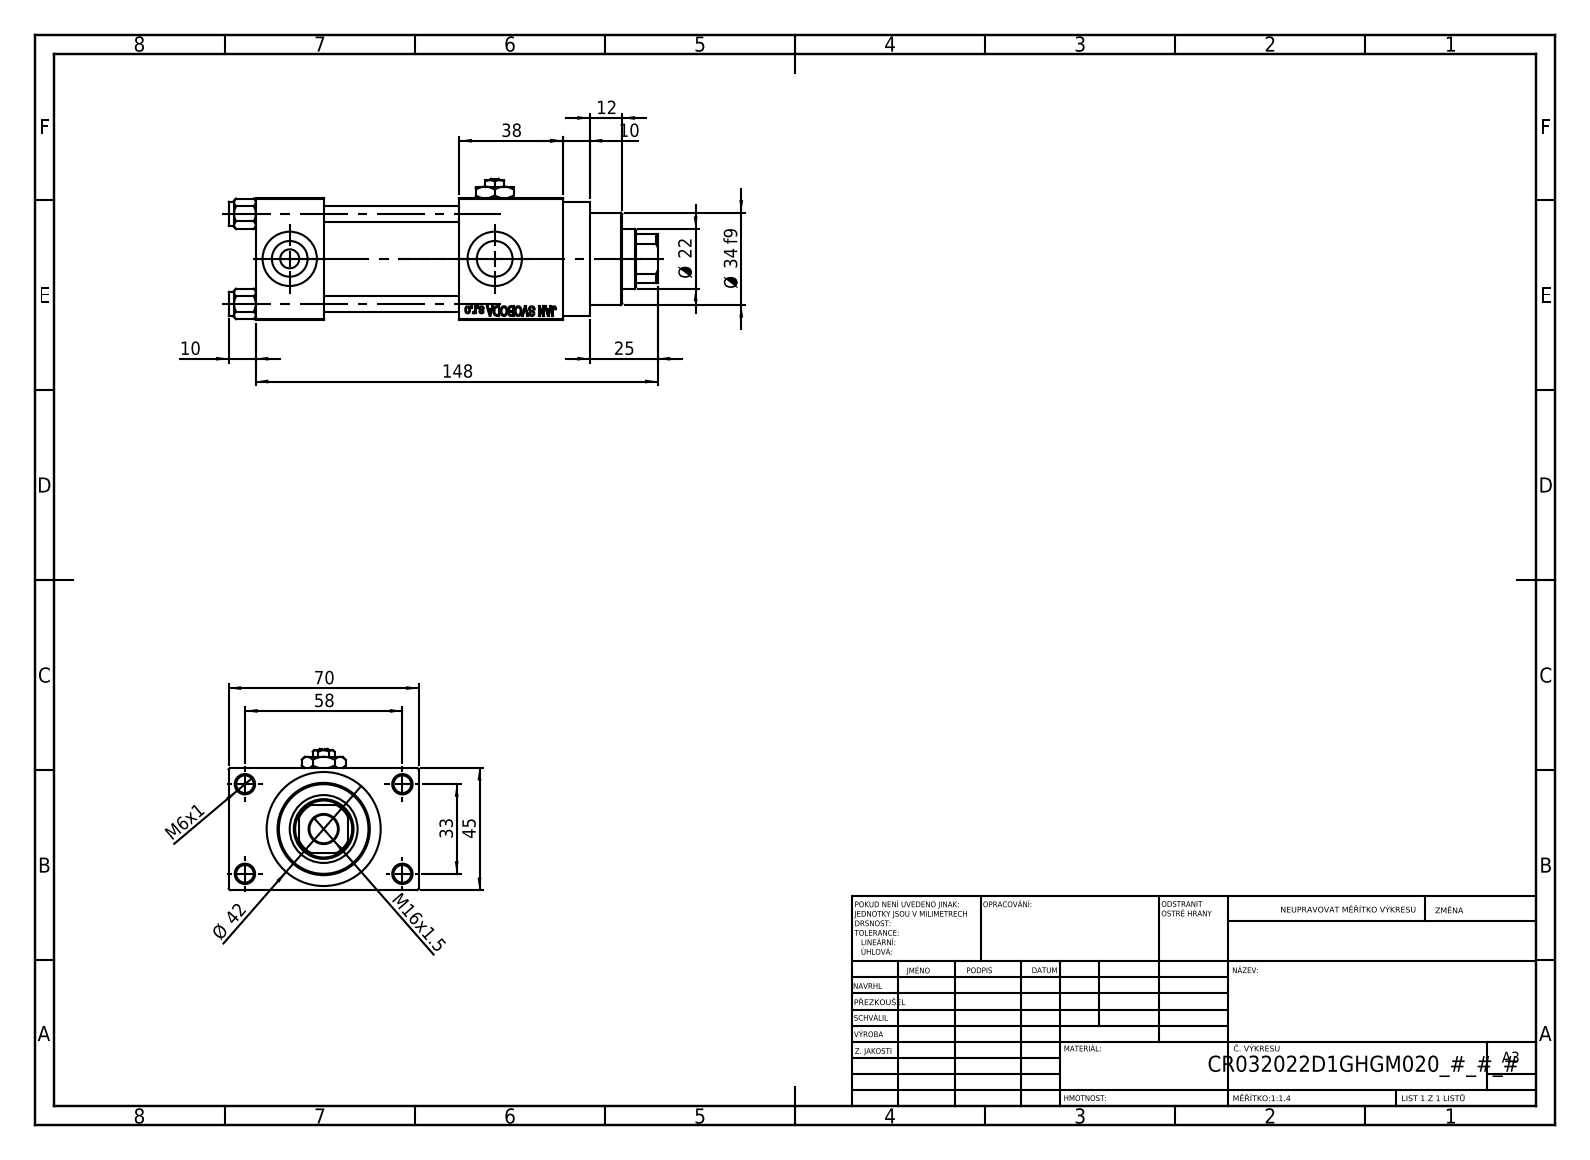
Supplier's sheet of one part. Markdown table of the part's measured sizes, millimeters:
| quantity | value |
| --- | --- |
| part name | V215CR_D_Body; NUT_M5_D; V215_VC_A; V215CR_D_TYCINKA (+2 more) |
| STEP written by | SolidWorks 2019 (CONFIG_CONTROL_DESIGN) |
| units | millimeters |
| bodies | 12 solids, 1149 faces (519 planar, 92 cylindrical, 538 other) |
| overall size | 158 × 70 × 52 |
| volume | 242 919 mm³ |
| surface area | 80 573 mm² |
| round holes (diameter × count) | 6 × 4, 6.5 × 4, 13.16 × 3, 20 × 3, 7 × 2, 10.5 × 1, 22 × 1, 24 × 1, 25 × 1, 32 × 1, 33 × 1 |
| round bosses / shafts (diameter × count) | 9 × 4, 42 × 1, 38 × 1, 34 × 1 |
| partial cylindrical surfaces (radius × count) | 10.5 × 1 |
| main face-to-face distances | 45, 25, 50, 12.5, 75, 57.5, 88, 38, 113, 70 |
| hole center spacings | 12.4, 23.48, 33.2, 33.37, 35.35, 45.6, 56.35, 33 |
